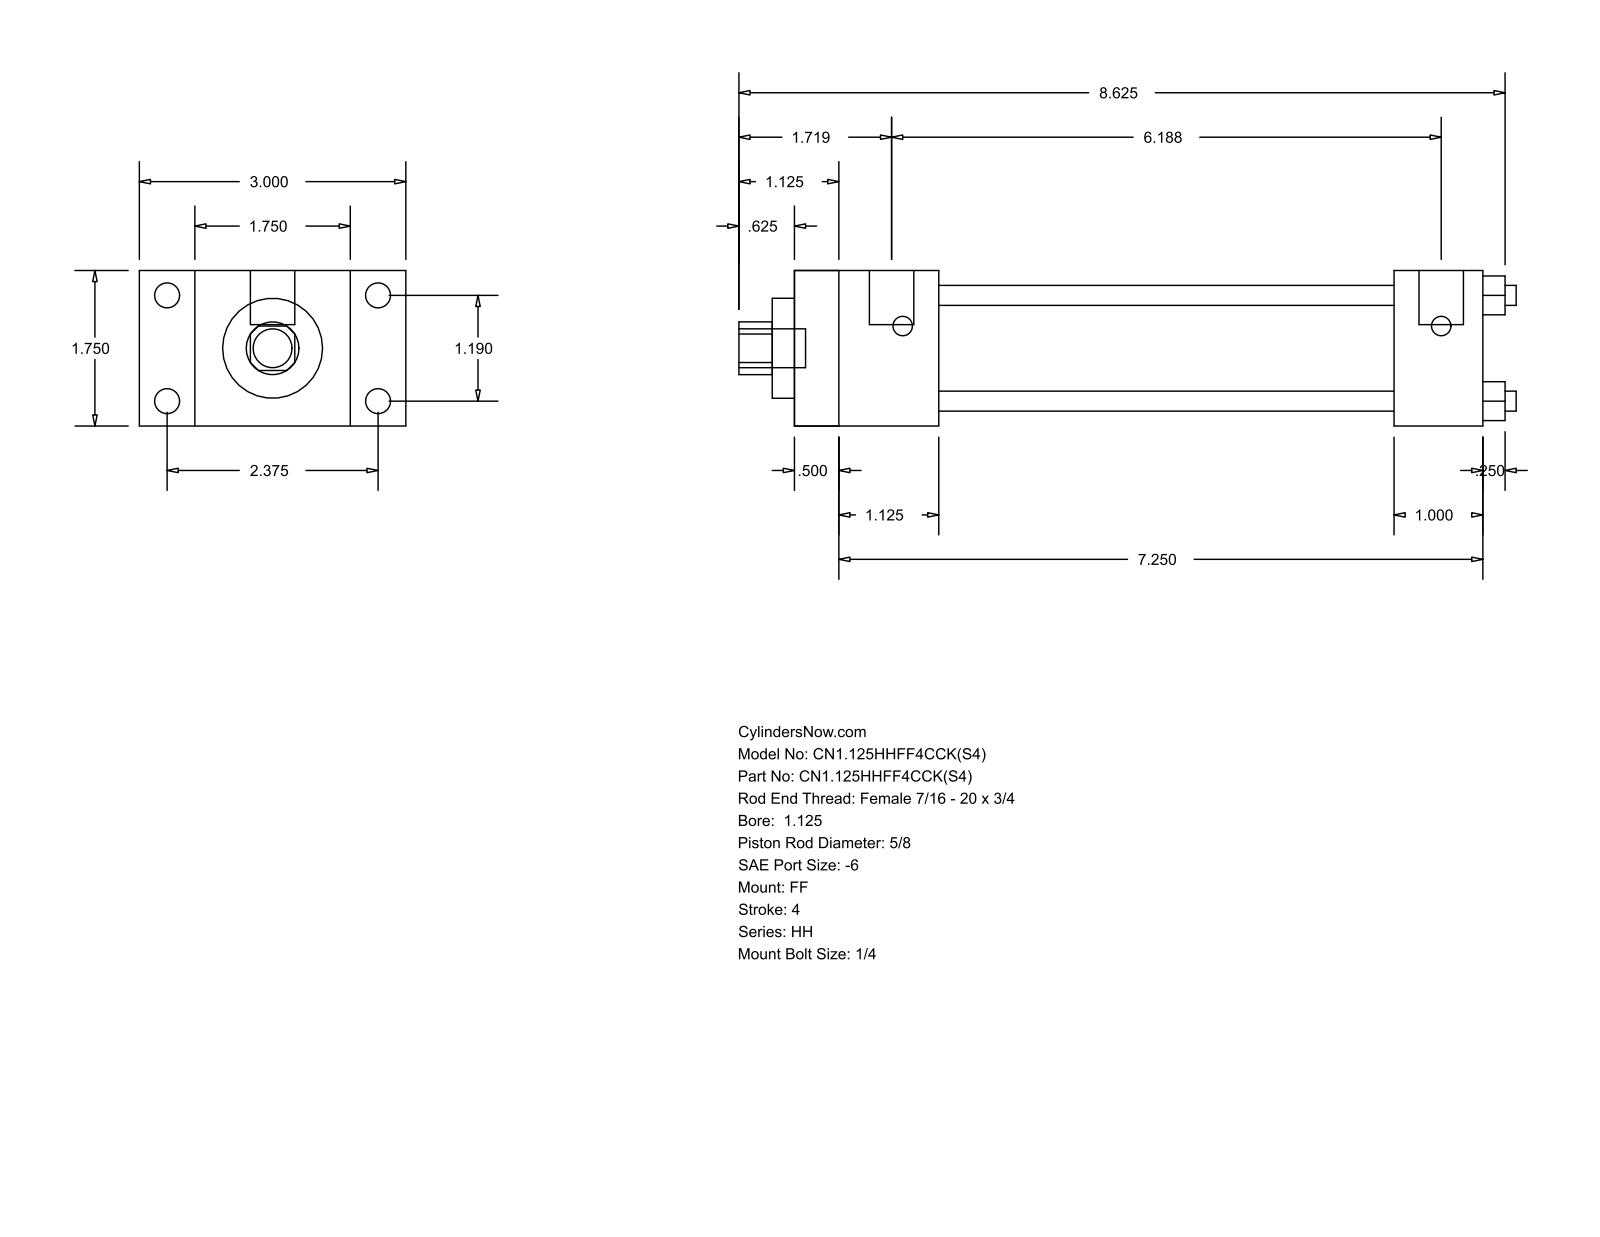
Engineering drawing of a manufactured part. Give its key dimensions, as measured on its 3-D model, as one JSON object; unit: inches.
{"part_name": "HH_FF__0112_0.625", "step_written_by": "GSSL Pune (CONFIG_CONTROL_DESIGN)", "units": "inches", "bodies": {"solids": 0, "faces": 92, "planar": 64, "cylindrical": 28, "other": 0}, "overall_size": [8.75, 3, 1.75], "round_holes": [[0.225, 4], [0.625, 1], [1.125, 1], [1.375, 1]], "round_bosses_or_shafts": [[0.281, 4], [0.219, 4], [0.5, 2], [0.437, 1]], "partial_cylinders_radius": [[0.297, 1]], "face_to_face_distances": [1.75, 7.75, 0.5, 7.25, 0.625, 2.375, 1.125, 1.625, 6.75, 6.25], "hole_center_spacings": [0.841, 1.19, 1.683]}
